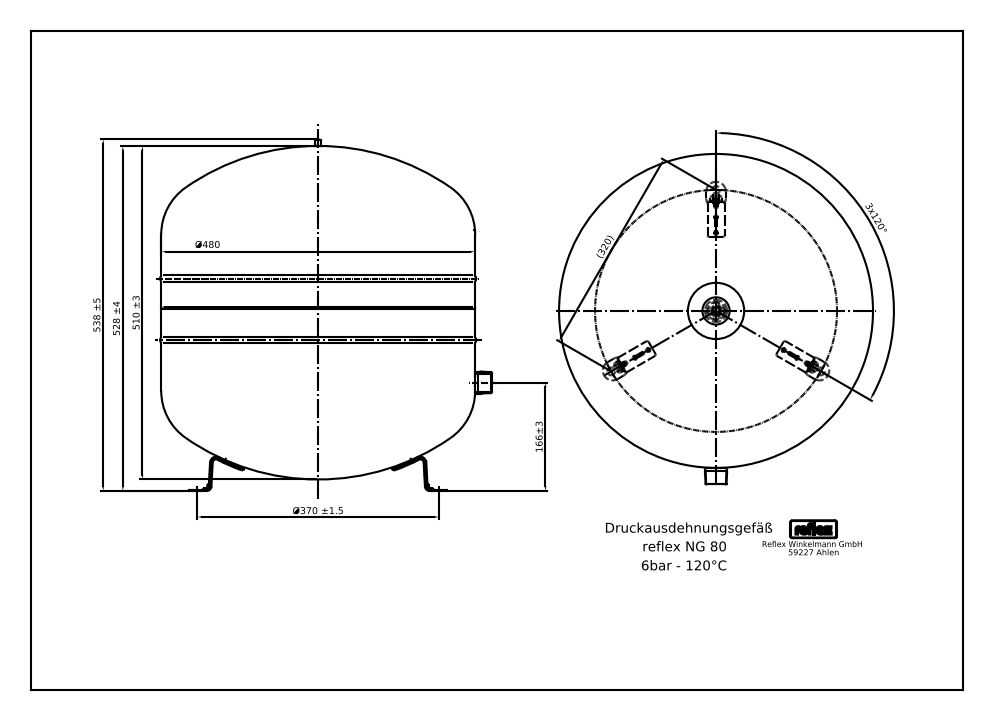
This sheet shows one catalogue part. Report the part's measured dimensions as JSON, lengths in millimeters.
{"step_written_by": "Mechanical Desktop 2011 (CONFIG_CONTROL_DESIGN)", "units": "millimeters", "bodies": {"solids": 16, "faces": 191, "planar": 76, "cylindrical": 74, "other": 41}, "overall_size": [565, 521, 512], "volume_mm3": 80680000, "surface_area_mm2": 1789000, "round_holes": [[15, 3], [25.7, 1]], "round_bosses_or_shafts": [[512, 1], [480, 1], [33.7, 1], [10, 1], [6, 1]], "partial_cylinders_radius": [[148.38, 9], [150.38, 9], [15, 6], [2.81, 4], [1.12, 3], [1.92, 2], [3.38, 2], [4.64, 2]], "face_to_face_distances": [275, 126.75, 148.25, 21.5, 275.75, 149, 297.25, 424, 2, 147], "hole_center_spacings": [320.43, 320.42]}
